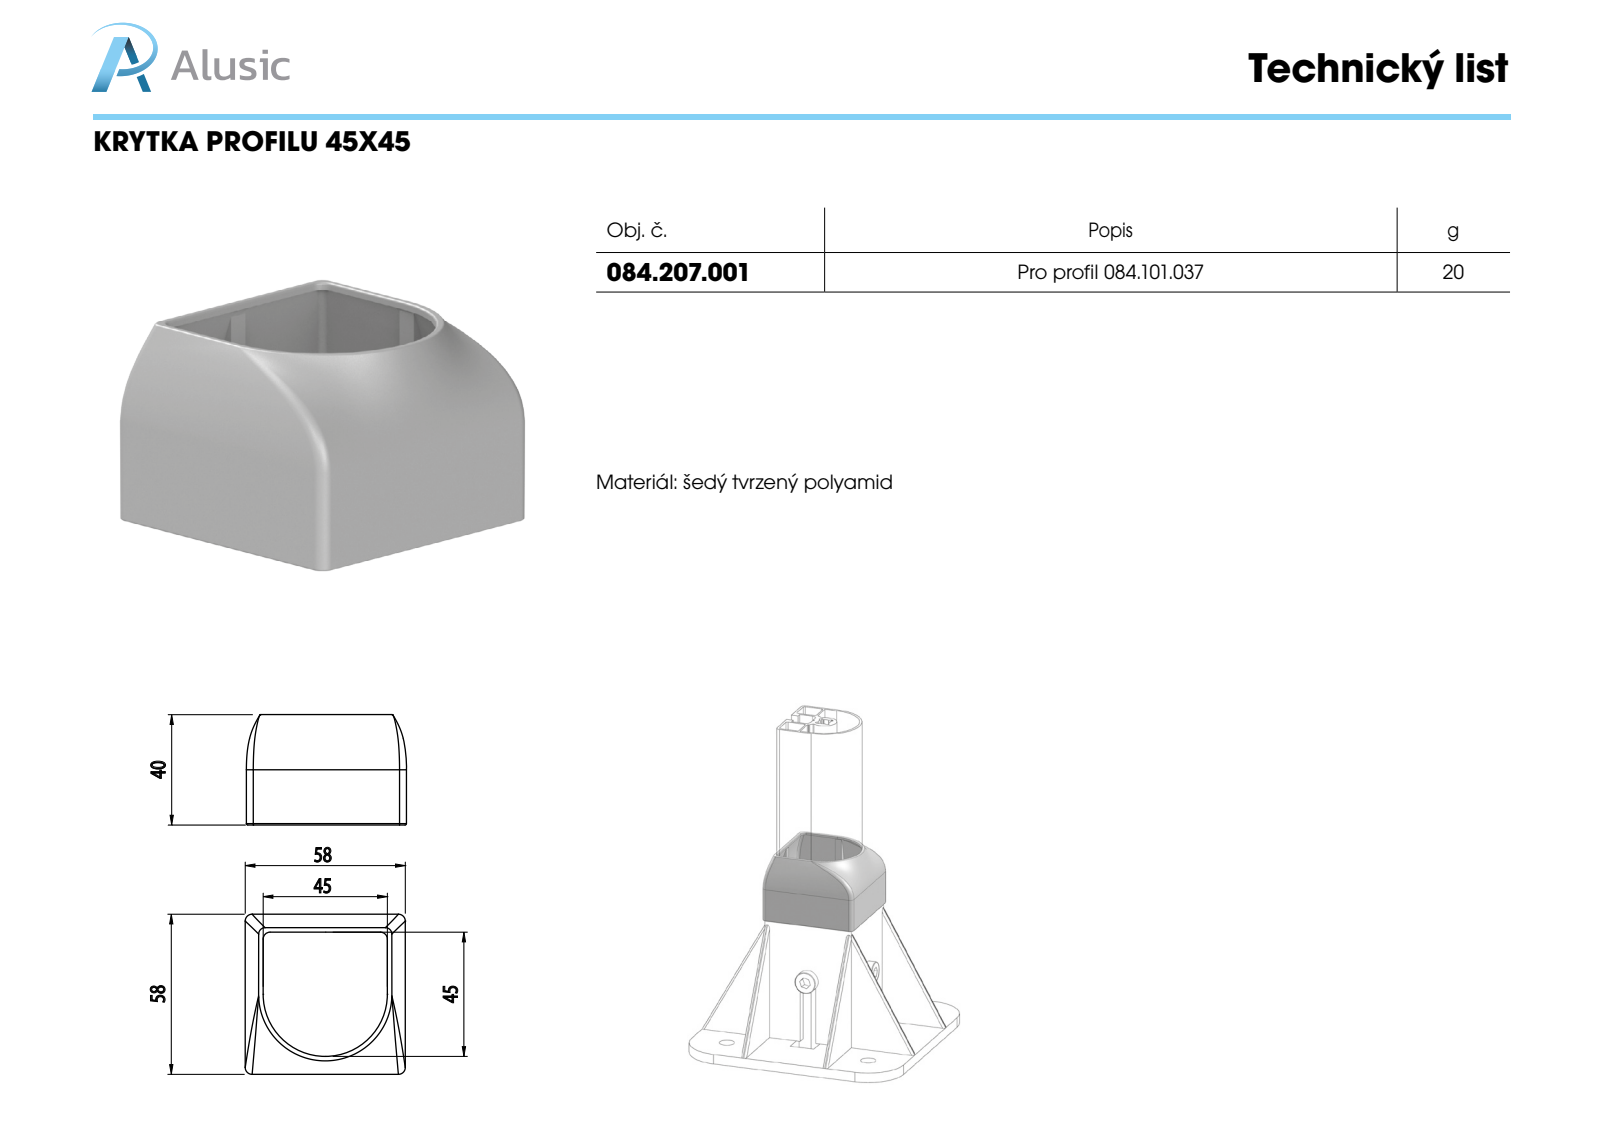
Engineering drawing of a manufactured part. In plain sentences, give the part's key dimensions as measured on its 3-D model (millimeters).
The part is named "084.207.001". Its 3-D file was written by "SolidWorks 2011 (CONFIG_CONTROL_DESIGN)". It is 1 solid with 87 faces: 30 planar, 22 cylindrical and 35 other. Overall it measures 58 by 58 by 40 millimeters. Its volume is 13 962 cubic millimeters and its surface area 18 458 square millimeters. Partial cylindrical surfaces (rounded edges, fillets, slot ends): 11 of radius 0.5, 6 of radius 2.5, 4 of radius 1.5, 1 of radius 22.5. The main face-to-face distances are 1.5, 56.5, 58, 55, 25.5, 4, 27, 31, 29.5, 5.5.
